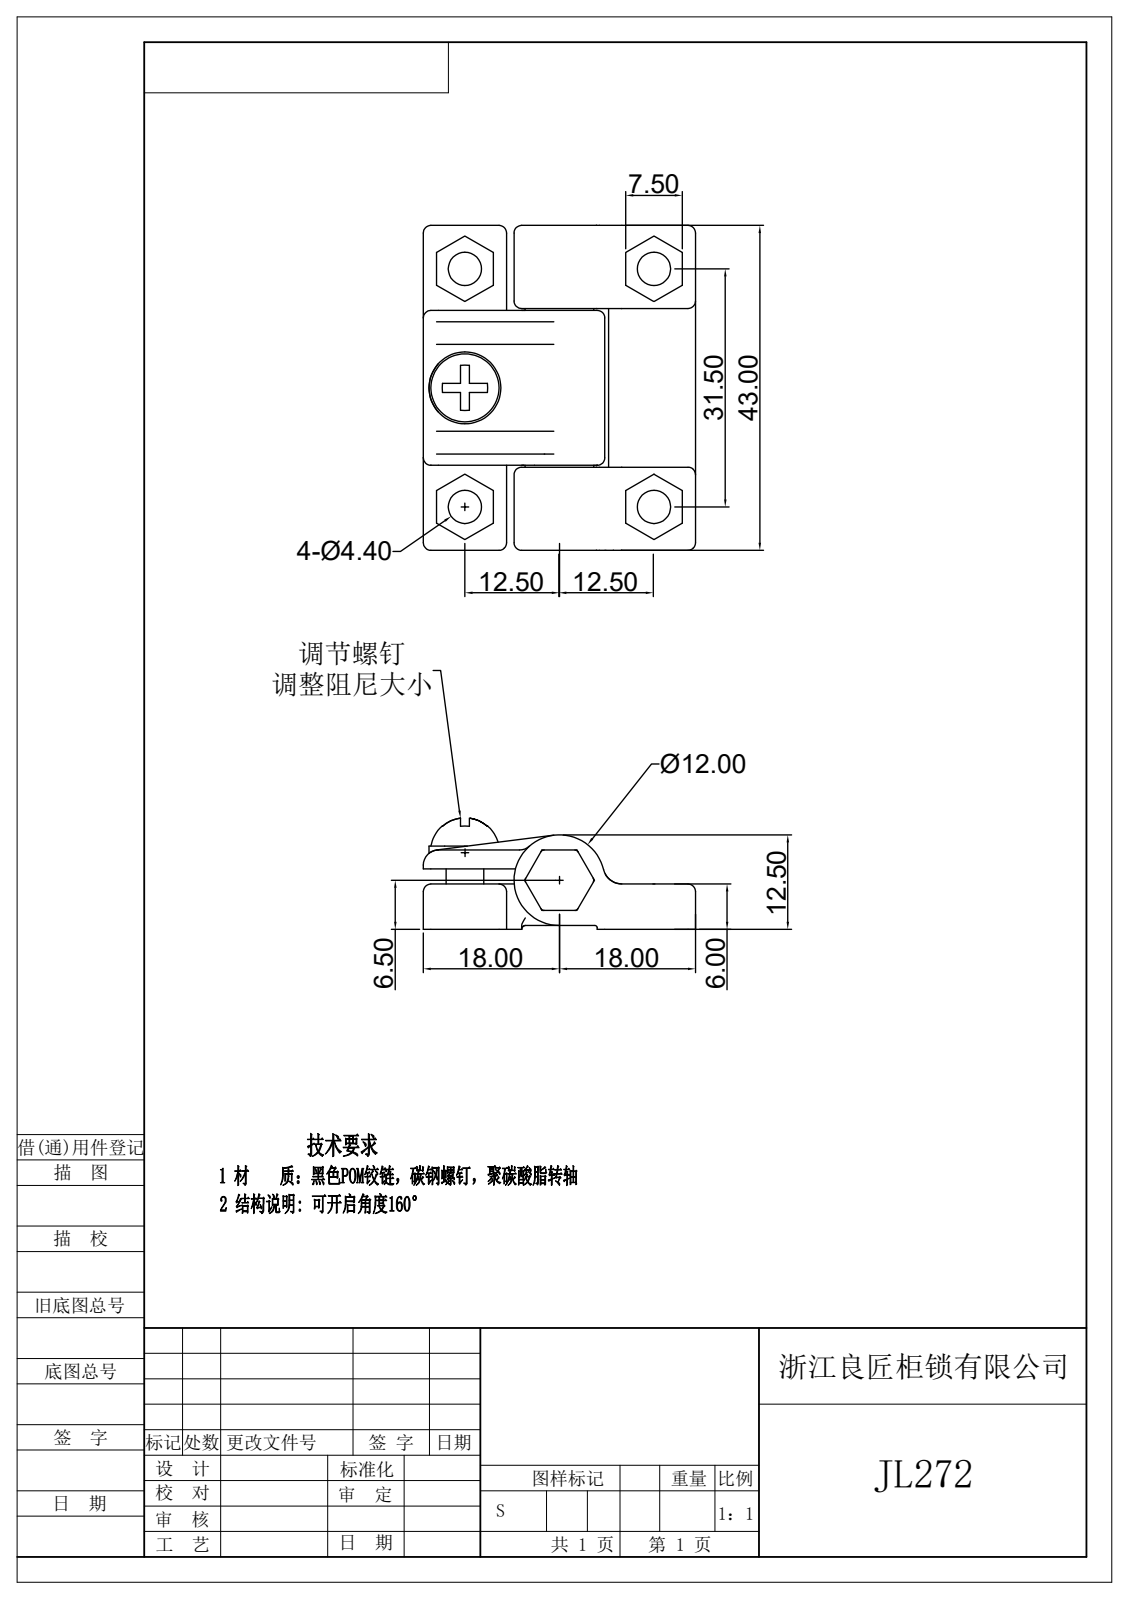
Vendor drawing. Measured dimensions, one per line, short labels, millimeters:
written by: Rhino 8.5 (CONFIG_CONTROL_DESIGN)
unit: mm
bodies: 7 solids, 359 faces (147 planar, 131 cylindrical, 81 other)
size: 134.24 × 119.51 × 28.86
volume: 9 746 mm³; area: 9 040 mm²
holes: 4× ⌀4.4, 1× ⌀4.13, 1× ⌀5.2, 1× ⌀6.2, 1× ⌀8
bosses: 1× ⌀12, 1× ⌀9.5, 1× ⌀5
rounds: 34× R0.5, 31× R1, 10× R0.3, 4× R1.18, 3× R2.5, 2× R2, 2× R6
face distances: 8, 2.5, 2, 6, 0.5, 10.5, 4.5, 3, 7.5, 5.5
hole spacings: 15.75, 25, 29.55, 31.5, 40.22
